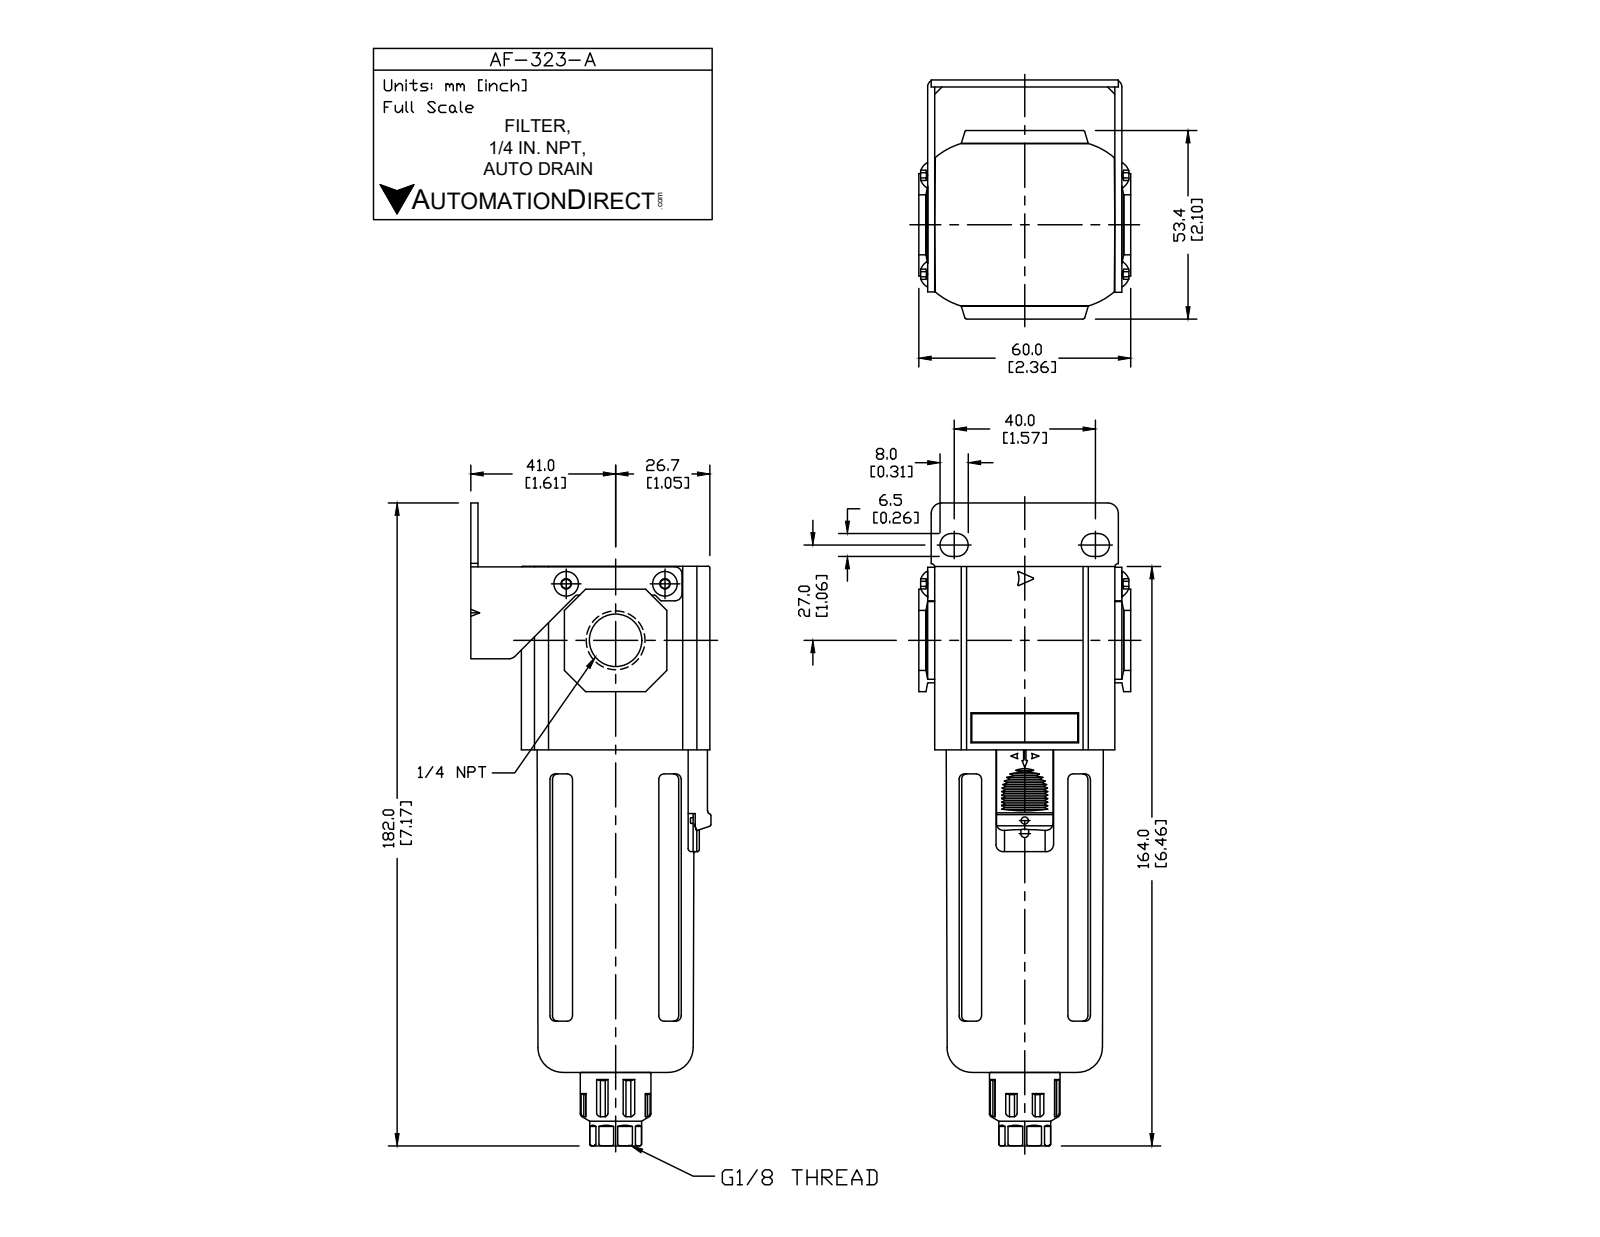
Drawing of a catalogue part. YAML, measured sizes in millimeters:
part_name: "AF-323-A"
step_written_by: "SolidWorks 2015 (CONFIG_CONTROL_DESIGN)"
units: millimeters
bodies: {solids: 9, faces: 390, planar: 246, cylindrical: 94, other: 50}
overall_size: [182.3, 67.7, 60]
volume: 206183
surface_area: 60574
round_holes:
  - {diameter: 3.4, count: 2}
  - {diameter: 8.57, count: 1}
  - {diameter: 11.13, count: 1}
  - {diameter: 35.99, count: 1}
  - {diameter: 44.8, count: 1}
round_bosses_or_shafts:
  - {diameter: 44.47, count: 1}
  - {diameter: 26, count: 1}
  - {diameter: 22.24, count: 1}
  - {diameter: 14.82, count: 1}
partial_cylinders:
  - {radius: 1, count: 18}
  - {radius: 2, count: 8}
  - {radius: 9.5, count: 8}
  - {radius: 0.5, count: 6}
  - {radius: 0.3, count: 4}
  - {radius: 3.25, count: 4}
  - {radius: 20, count: 4}
  - {radius: 0.2, count: 3}
face_to_face_distances: [2, 51, 2.5, 53, 12.3, 67.7, 65.7, 14.3, 53.4, 55.5]
hole_center_spacings: [21.06, 21.46, 28]
